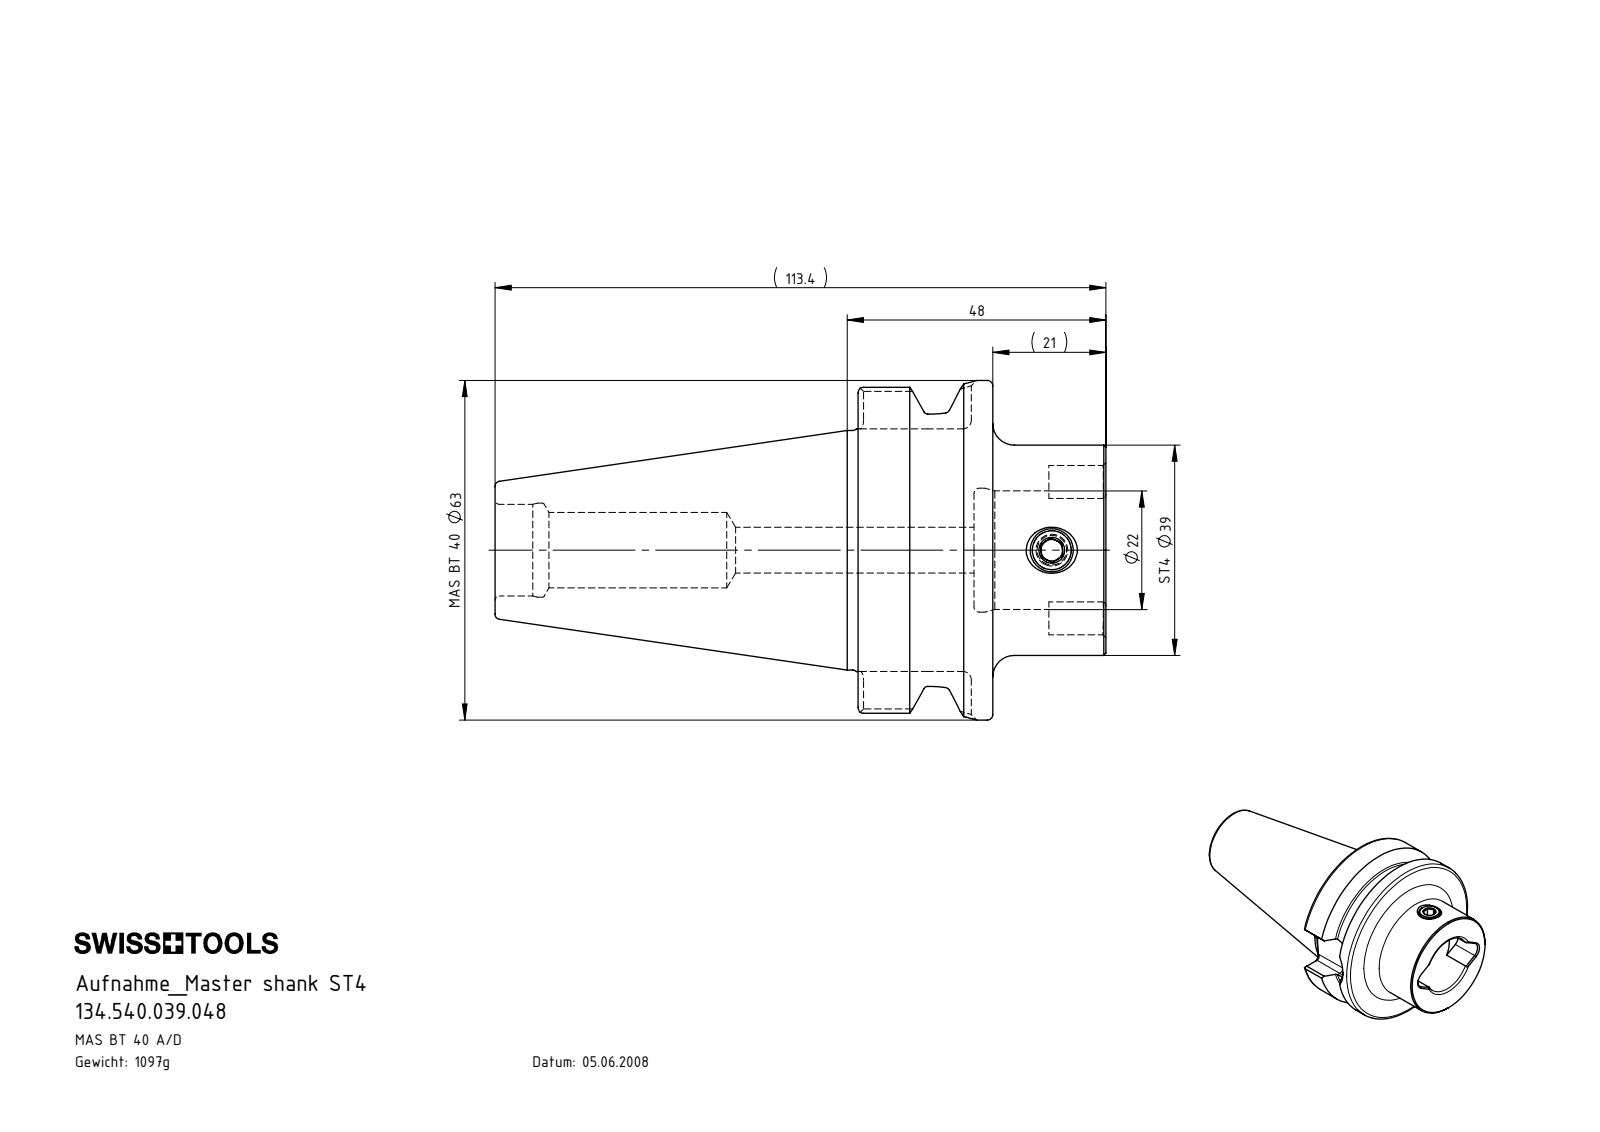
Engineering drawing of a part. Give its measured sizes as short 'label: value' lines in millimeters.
name: BT4-ST4.K01.048; BT4-ST4.K01.048_A; ST4-ER1.001.011_A
written by: SolidWorks 2015 (CONFIG_CONTROL_DESIGN)
unit: mm
bodies: 2 solids, 136 faces (36 planar, 40 cylindrical, 60 other)
size: 113.4 × 63 × 63
volume: 139 730 mm³; area: 26 011 mm²
holes: 1× ⌀7.25, 1× ⌀8.5, 1× ⌀14, 1× ⌀17, 1× ⌀17.45, 1× ⌀22, 1× ⌀23
bosses: 1× ⌀63, 1× ⌀53, 1× ⌀44.45, 1× ⌀39, 1× ⌀8
rounds: 8× R1.6, 2× R3.2, 1× R8.05
face distances: 25, 46, 21, 21.5, 3.5, 24.5, 45, 67.4, 88.9, 92.4
